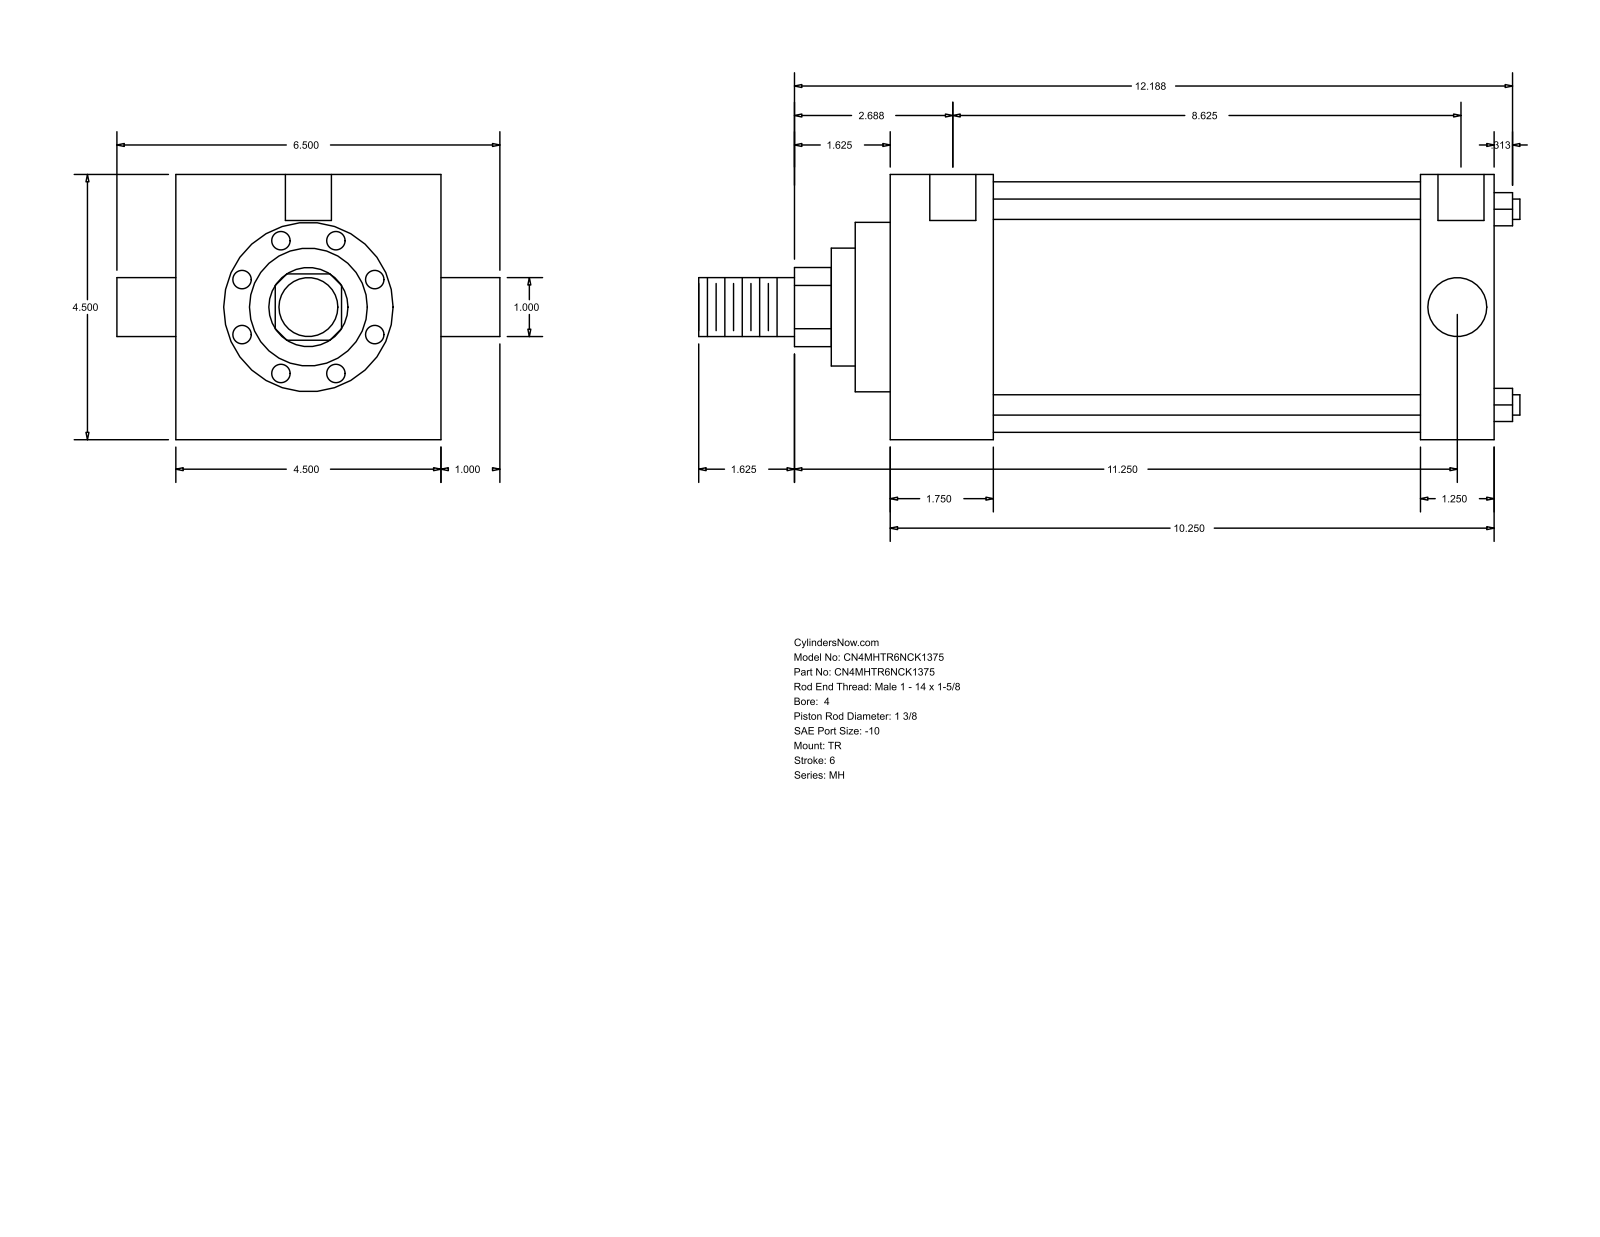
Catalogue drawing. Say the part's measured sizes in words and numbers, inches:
The part is named "MH_TR__0400_1.375". Its 3-D file was written by "GSSL Pune (CONFIG_CONTROL_DESIGN)". It is 0 solids with 86 faces: 61 planar, 25 cylindrical and 0 other. Overall it measures 13.937 by 6.5 by 4.5 inches. Round holes: 3 of diameter 0.344, 2 of diameter 0.781. Round bosses or shafts: 4 of diameter 0.345, 2 of diameter 1, 1 of diameter 4.25, 1 of diameter 2.875, 1 of diameter 2, 1 of diameter 1.375. Partial cylindrical surfaces (rounded edges, fillets, slot ends): 1 of radius 0.672. The main face-to-face distances are 4.5, 10.25, 1.75, 8.5, 9, 7.25, 1.25, 0.594, 2.344, 9.594. The hole center spacings are 0.063, 8.688, 8.625, 8.75.
